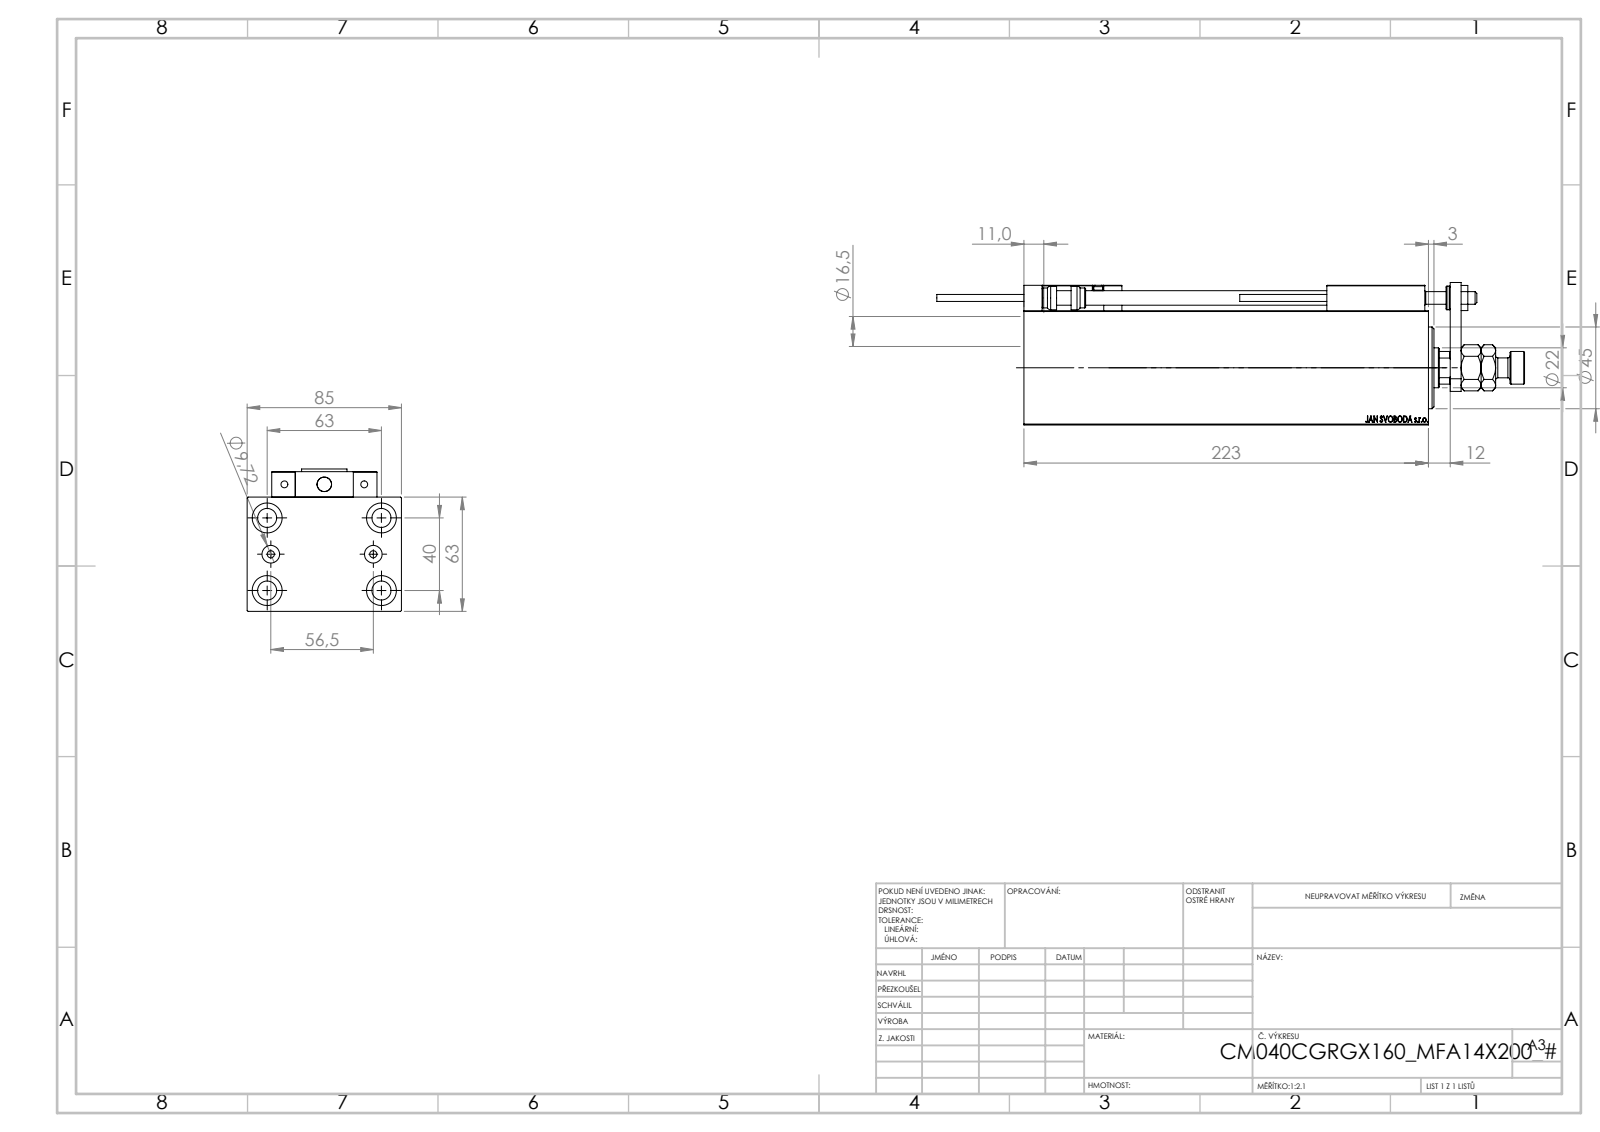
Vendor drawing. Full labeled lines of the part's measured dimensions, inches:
Part name (STEP PRODUCT): V450CM_C_Body; SWITCH DIM B,W; MAGNET; ZARAZKA (+7 more)
STEP written by: SolidWorks 2019 (CONFIG_CONTROL_DESIGN)
Units: inches
Bodies: 24 solids, 1330 faces (576 planar, 188 cylindrical, 566 other)
Overall size (bounding box): 12.756 × 3.346 × 3.091
Volume: 62.85 in³ · Surface area: 305.3 in²
Round holes (diameter × count): ⌀0.157 ×6, ⌀0.315 ×5, ⌀0.65 ×5, ⌀0.126 ×4, ⌀0.413 ×4, ⌀0.197 ×2, ⌀0.383 ×2, ⌀0.276 ×1, ⌀0.492 ×1, ⌀0.866 ×1, ⌀1.004 ×1, ⌀1.575 ×1
Round bosses / shafts (diameter × count): ⌀0.433 ×2, ⌀0.197 ×2, ⌀0.15 ×2, ⌀0.709 ×1, ⌀0.512 ×1
Partial cylindrical surfaces — rounded edges, fillets, slot ends (radius × count): R0.012 ×30, R0.118 ×2, R0.413 ×1
Main face-to-face distances: 2.48, 3.346, 0.472, 8.307, 8.78, 0.551, 0.709, 1.181, 3.031, 0.787
Hole centre spacings: 1.469, 0.448, 0.787, 0.791, 0.807, 1.165, 1.169, 1.42
